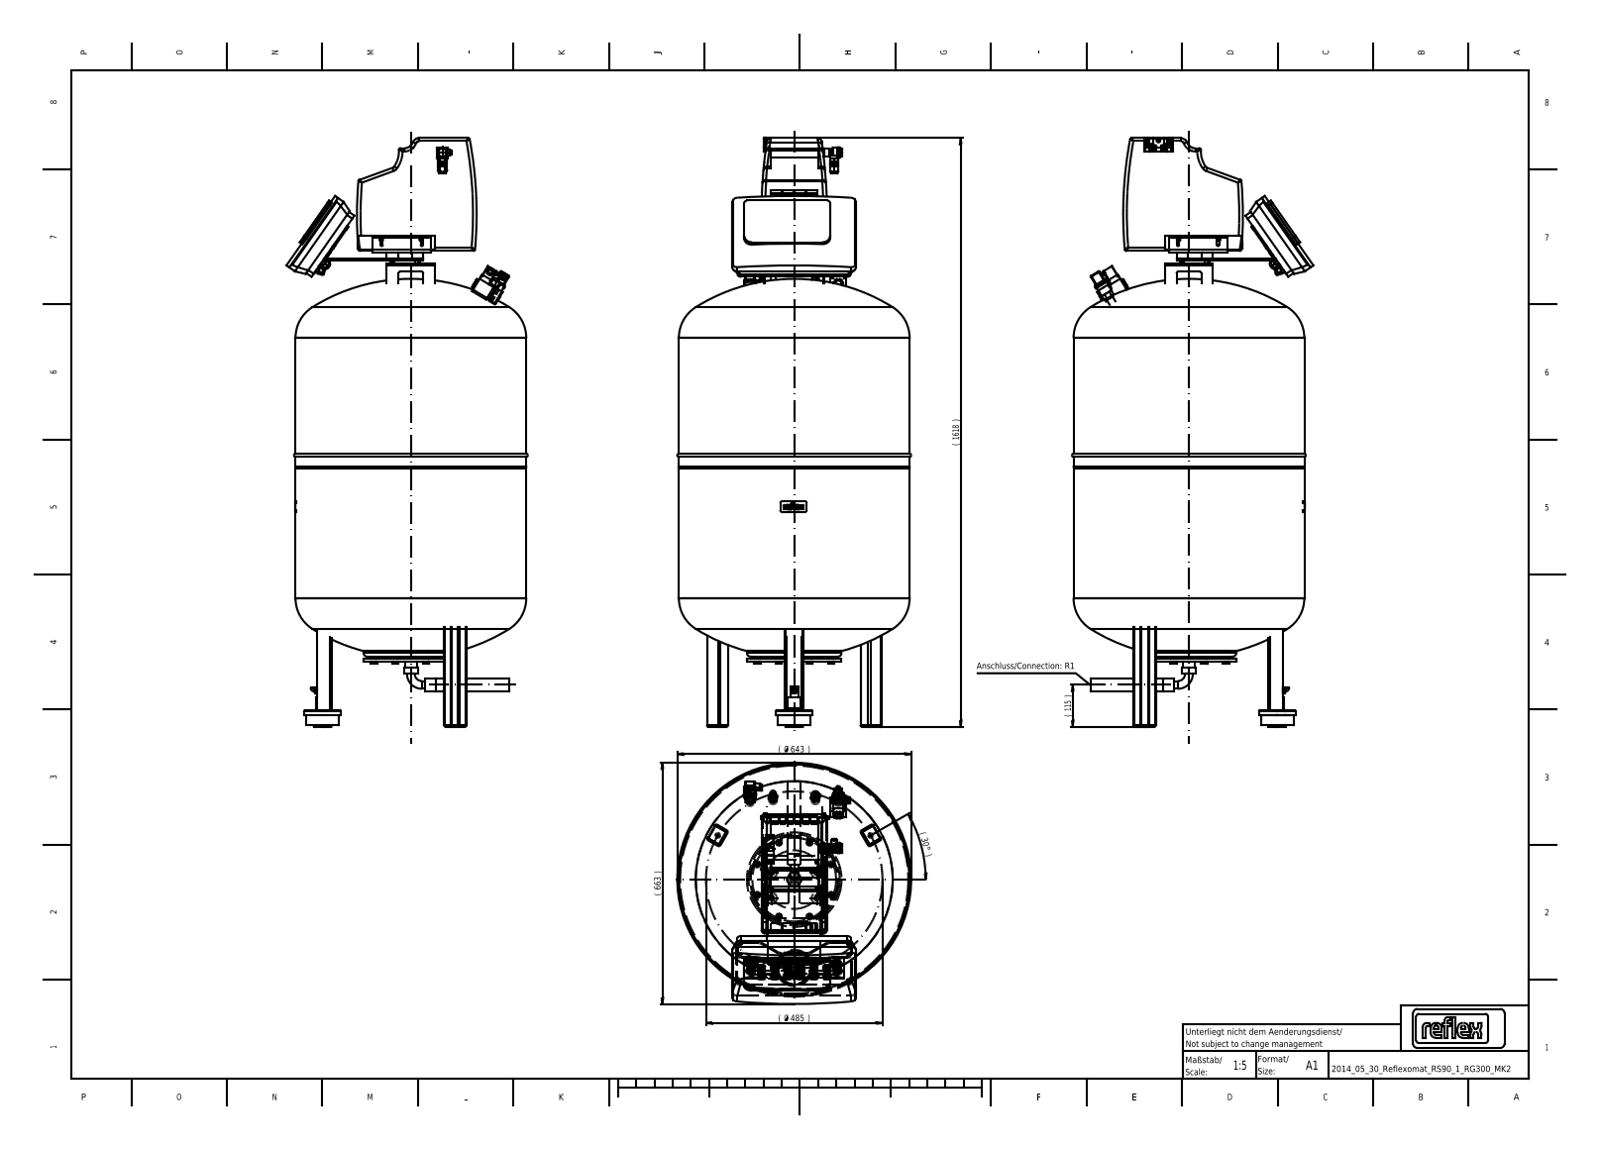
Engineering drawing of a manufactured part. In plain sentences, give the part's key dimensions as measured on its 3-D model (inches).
Its 3-D file was written by "CATIA V5 STEP AP214 (AUTOMOTIVE_DESIGN)". It is 41 solids with 2877 faces: 1967 planar, 548 cylindrical and 362 other. Overall it measures 63.701 by 26.115 by 25.307 inches. Its volume is 19 230 cubic inches and its surface area 8 331 square inches. Round holes: 8 of diameter 0.323, 8 of diameter 0.413, 7 of diameter 0.669, 4 of diameter 0.217, 4 of diameter 0.354, 2 of diameter 0.394, 2 of diameter 0.528, 1 of diameter 0.079, 1 of diameter 0.256, 1 of diameter 0.276, 1 of diameter 0.551, 1 of diameter 0.787. Round bosses or shafts: 10 of diameter 0.394, 8 of diameter 0.748, 8 of diameter 0.63, 8 of diameter 0.315, 7 of diameter 0.689, 4 of diameter 1.181, 3 of diameter 0.839, 3 of diameter 0.78. Partial cylindrical surfaces (rounded edges, fillets, slot ends): 31 of radius 0.098, 23 of radius 0.197, 14 of radius 0.315, 11 of radius 0.394, 10 of radius 0.039, 6 of radius 0.118, 4 of radius 0.155, 4 of radius 0.177. The main face-to-face distances are 28.189, 0.157, 0.098, 0.866, 0.079, 6.575, 34.764, 1.87, 0.236, 6.811. The hole center spacings are 4.921, 1.417, 2.835, 4.927, 4.997, 5.043, 4.252, 5.64.
